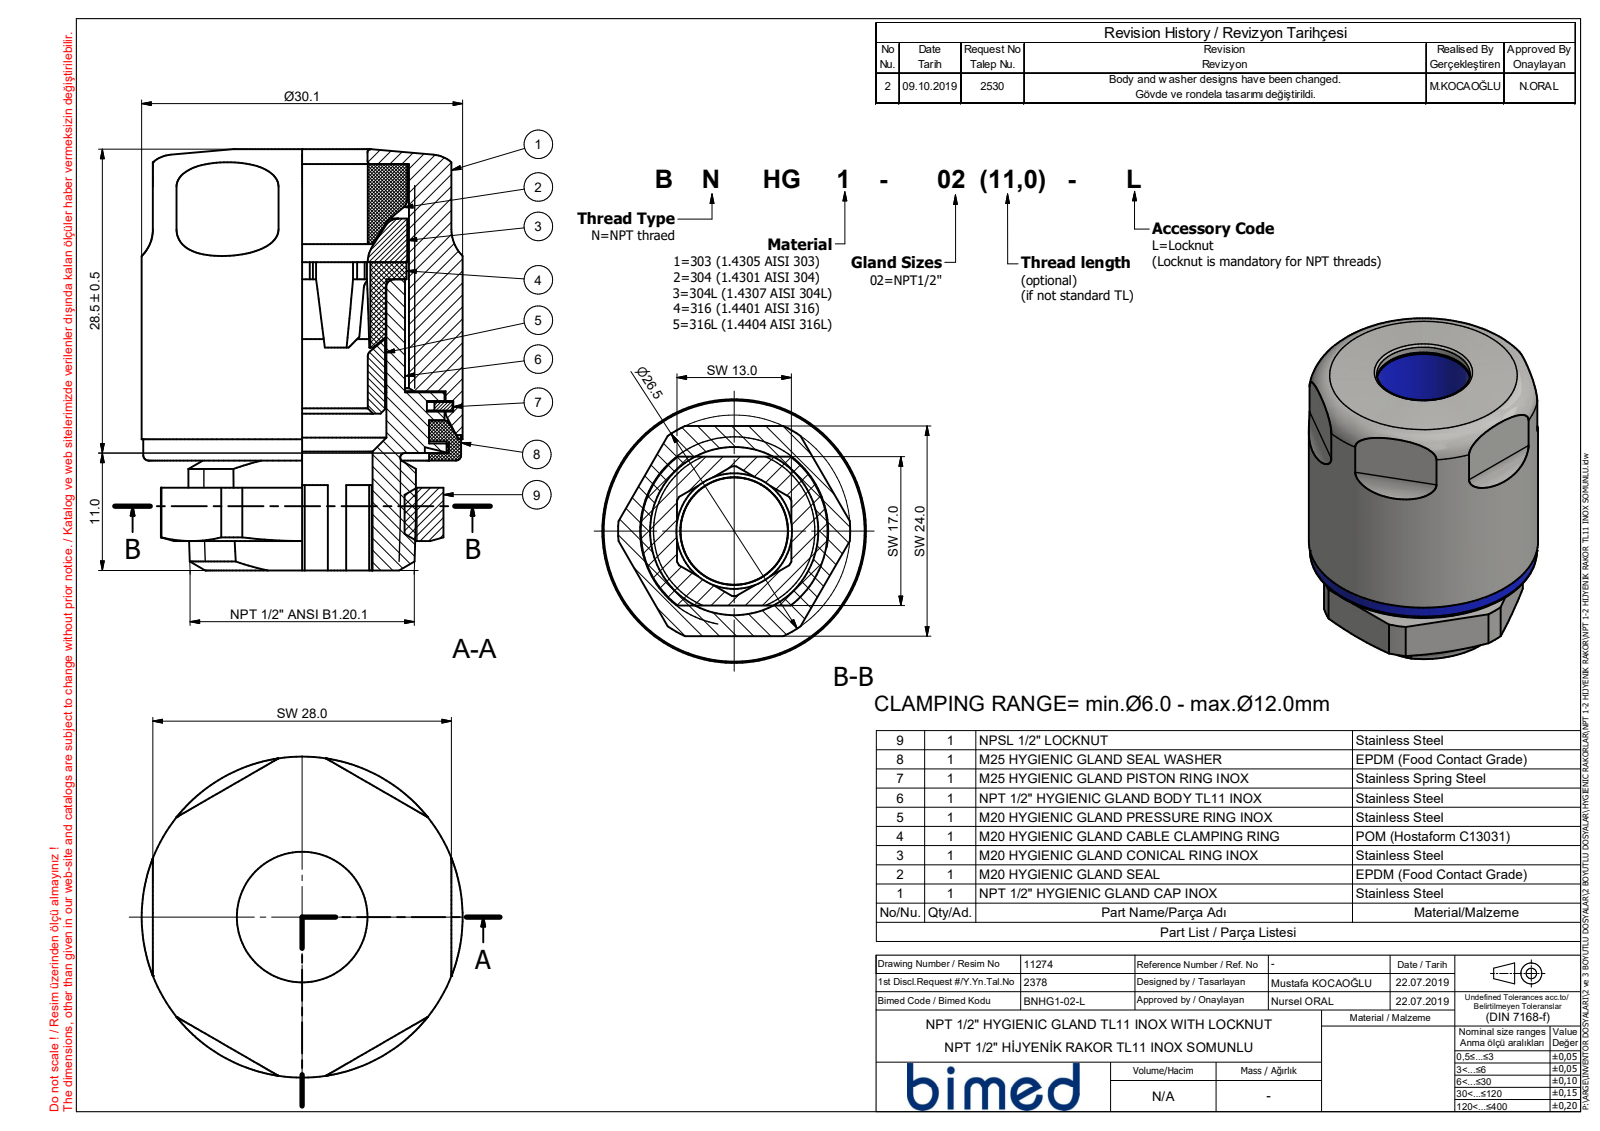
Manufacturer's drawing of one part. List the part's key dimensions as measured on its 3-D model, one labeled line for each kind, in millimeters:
Part name (STEP PRODUCT): BNHG1-02-L
STEP written by: SolidWorks 2021 (CONFIG_CONTROL_DESIGN)
Units: millimetres
Bodies: 1 solid, 57 faces (15 planar, 10 cylindrical, 32 other)
Overall size (bounding box): 40.1 × 30.1 × 30.1
Volume: 24 480 mm³ · Surface area: 5 132 mm²
Round bosses / shafts (diameter × count): ⌀30.1 ×1, ⌀29.8 ×1
Partial cylindrical surfaces — rounded edges, fillets, slot ends (radius × count): R13.3 ×1
Main face-to-face distances: 10.3, 7.8, 2.5, 24, 2.8, 5, 7.5, 3.5, 20.5, 17
